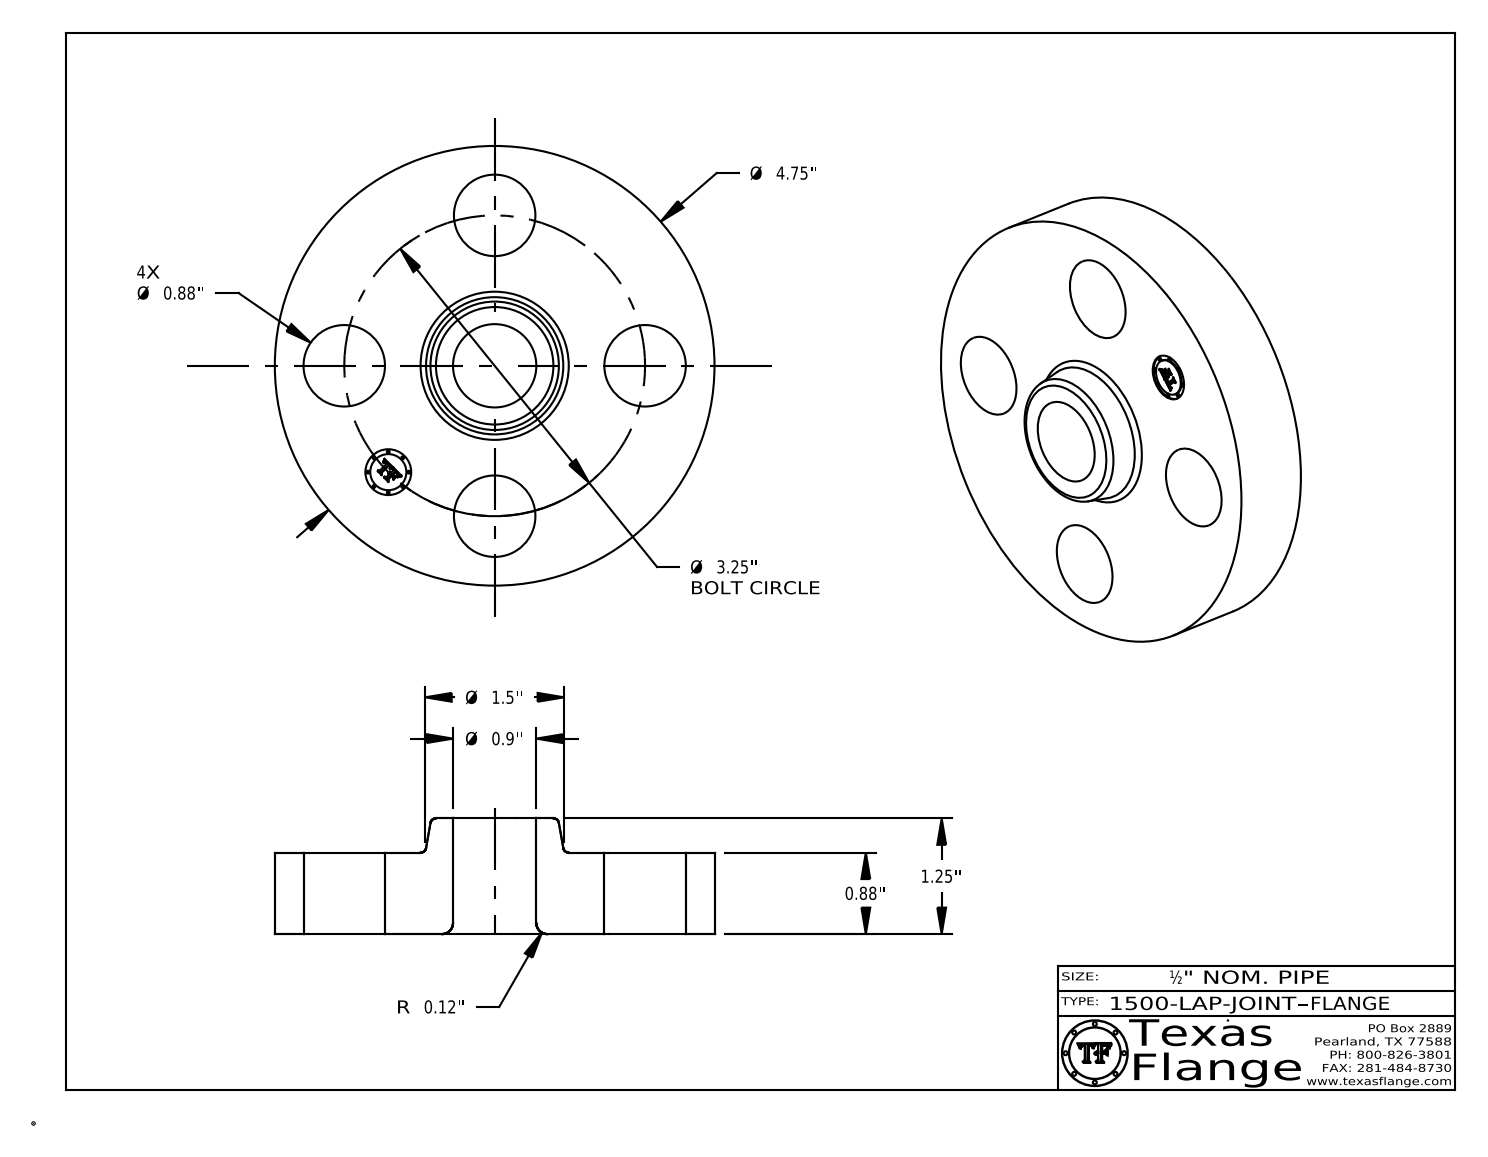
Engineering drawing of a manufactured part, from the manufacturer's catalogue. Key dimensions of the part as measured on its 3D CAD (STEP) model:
Part name (STEP PRODUCT): 1500-LAP-JOINT FLANGE
STEP written by: CATIA V5 STEP AP214 (AUTOMOTIVE_DESIGN)
Units: inches
Bodies: 1 solid, 408 faces (368 planar, 32 cylindrical, 8 other)
Overall size (bounding box): 4.75 × 4.75 × 1.25
Volume: 13.25 in³ · Surface area: 56.9 in²
Round holes (diameter × count): ⌀0.88 ×4, ⌀0.495 ×1, ⌀0.9 ×1
Round bosses / shafts (diameter × count): ⌀0.03 ×8, ⌀4.75 ×1, ⌀0.39 ×1
Main face-to-face distances: 0.88, 1.25, 0.37, 0.865, 0.015, 0.385, 0.148, 0.144, 0.027, 0.096
Hole centre spacings: 1.625, 2.298, 1.244, 3.003, 3.25
